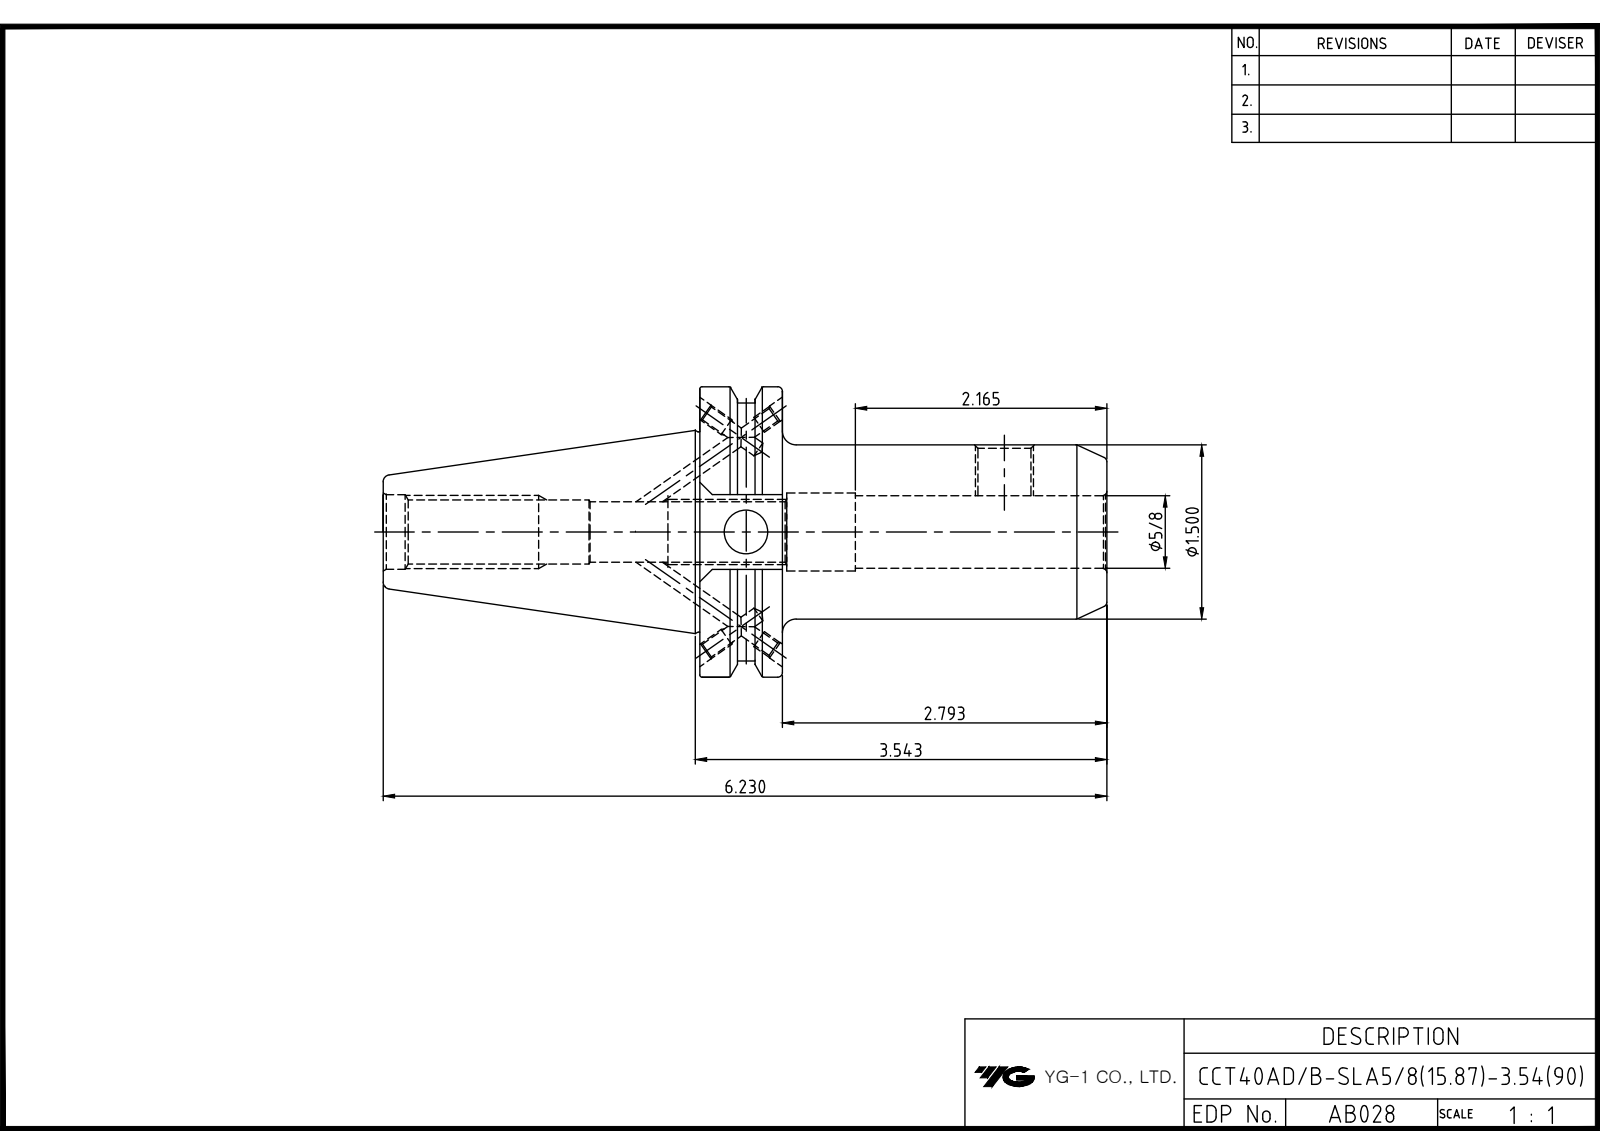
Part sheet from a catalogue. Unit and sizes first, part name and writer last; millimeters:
Units: millimetres
Overall size (bounding box): 158.25 × 63.5 × 61.09
Round holes (diameter × count): ⌀3.24 ×4, ⌀4 ×4, ⌀9.53 ×1, ⌀11.33 ×1, ⌀12.57 ×1, ⌀13.39 ×1, ⌀15.88 ×1, ⌀16.3 ×1, ⌀17.07 ×1
Round bosses / shafts (diameter × count): ⌀63.5 ×1, ⌀56.3 ×1, ⌀43.8 ×1, ⌀38.1 ×1
Main face-to-face distances: 18.05, 89, 70.95, 47.6, 16.38, 69.25, 87.3, 158.25, 77.46, 81.29
Hole centre spacings: 33.88
Volume: 168 272 mm³ · Surface area: 32 964 mm²
Bodies: 1 solid, 88 faces (36 planar, 27 cylindrical, 25 other)
Part name (STEP PRODUCT): LO-CCT40ADB-SLA15.875-90
STEP written by: Autodesk Inventor 2025 (AUTOMOTIVE_DESIGN)
